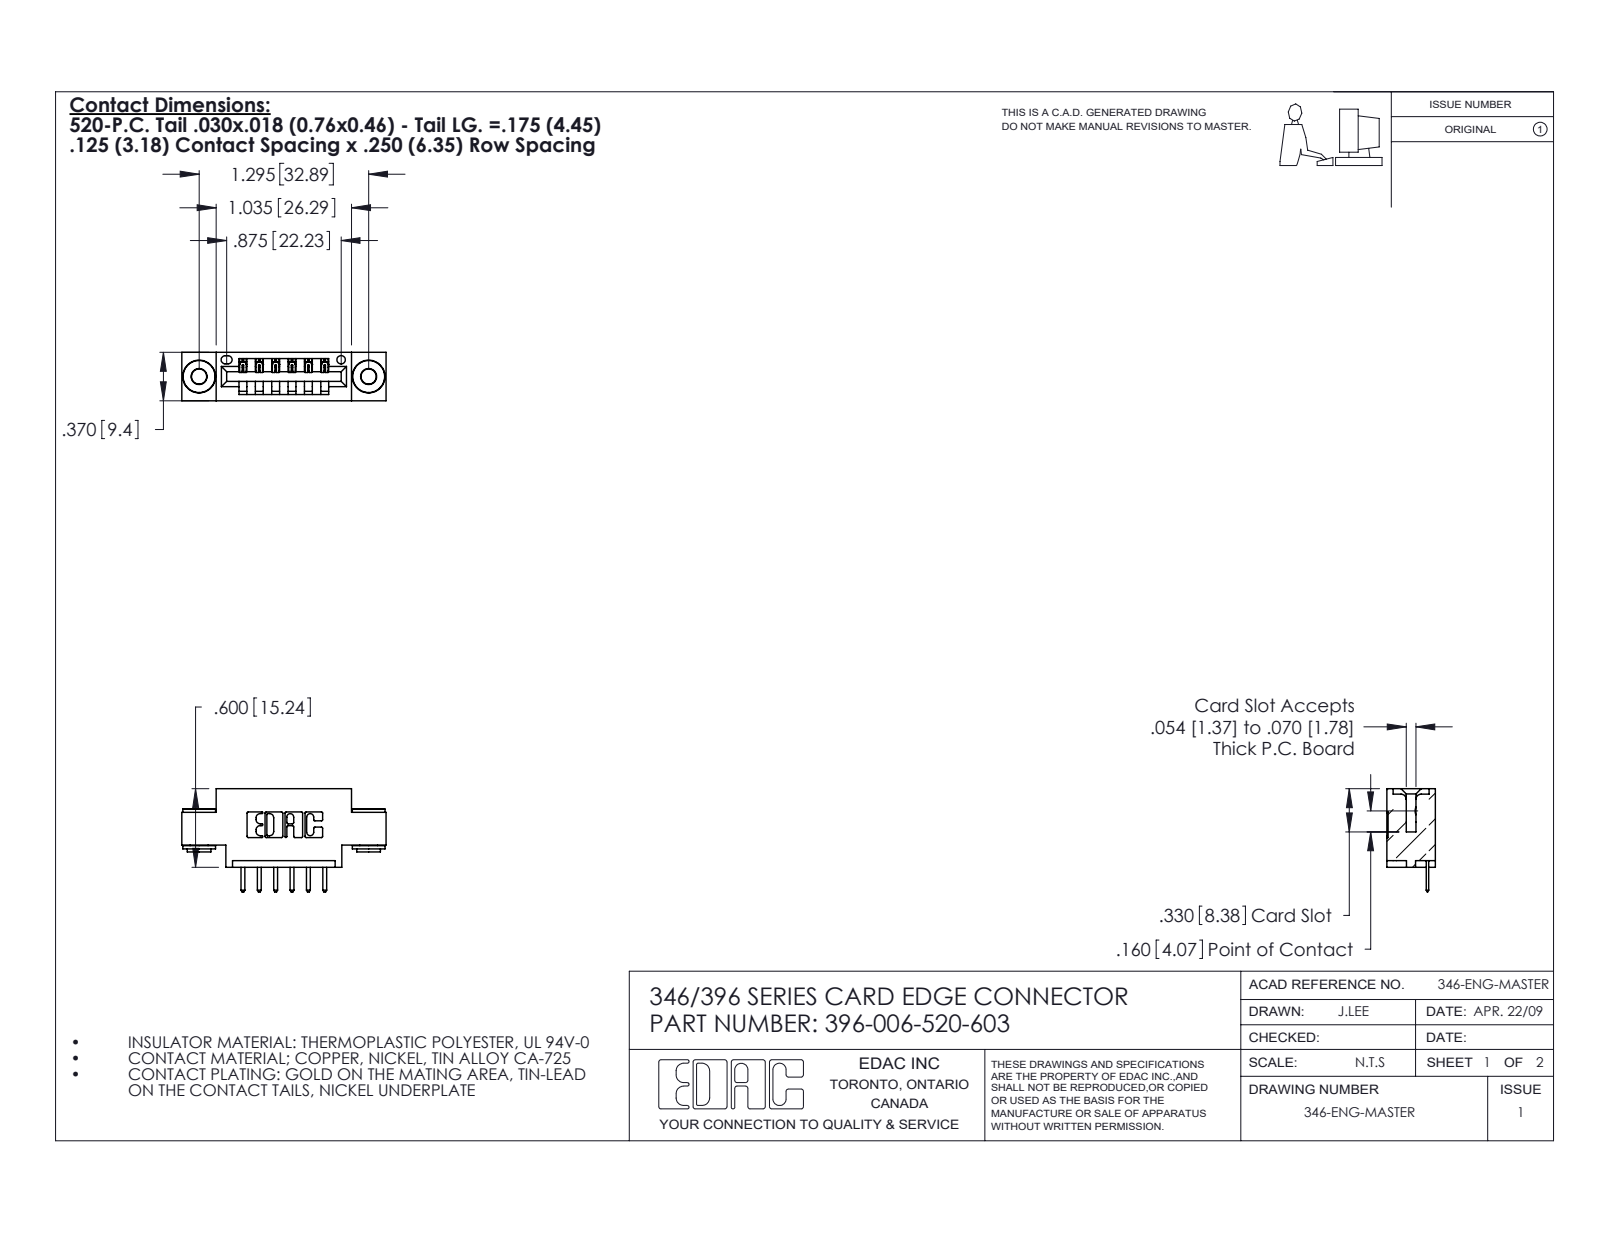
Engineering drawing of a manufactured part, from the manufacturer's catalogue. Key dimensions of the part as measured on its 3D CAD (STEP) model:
Part name (STEP PRODUCT): 345-250-002_345-250-002-102; 345-292-001_345-293-120; 396-006-520-603; 346 Part_0.170 Offset - 0.156 Dia-TH
STEP written by: SolidWorks 2020 (CONFIG_CONTROL_DESIGN)
Units: inches
Bodies: 9 solids, 550 faces (356 planar, 186 cylindrical, 8 other)
Overall size (bounding box): 1.56 × 0.788 × 0.37
Volume: 0.206 in³ · Surface area: 6.484 in²
Round holes (diameter × count): ⌀0.116 ×2, ⌀0.156 ×2, ⌀0.064 ×1
Round bosses / shafts (diameter × count): ⌀0.25 ×2, ⌀0.18 ×2, ⌀0.136 ×2
Partial cylindrical surfaces — rounded edges, fillets, slot ends (radius × count): R0.01 ×22, R0.01 ×14, R0.006 ×12, R0.007 ×6, R0.031 ×6, R0.026 ×3, R0.031 ×2, R0.04 ×2
Main face-to-face distances: 0.25, 0.37, 0.048, 0.322, 0.025, 0.222, 0.148, 0.1, 0.174, 0.125
Hole centre spacings: 0.246, 1.092, 1.295
